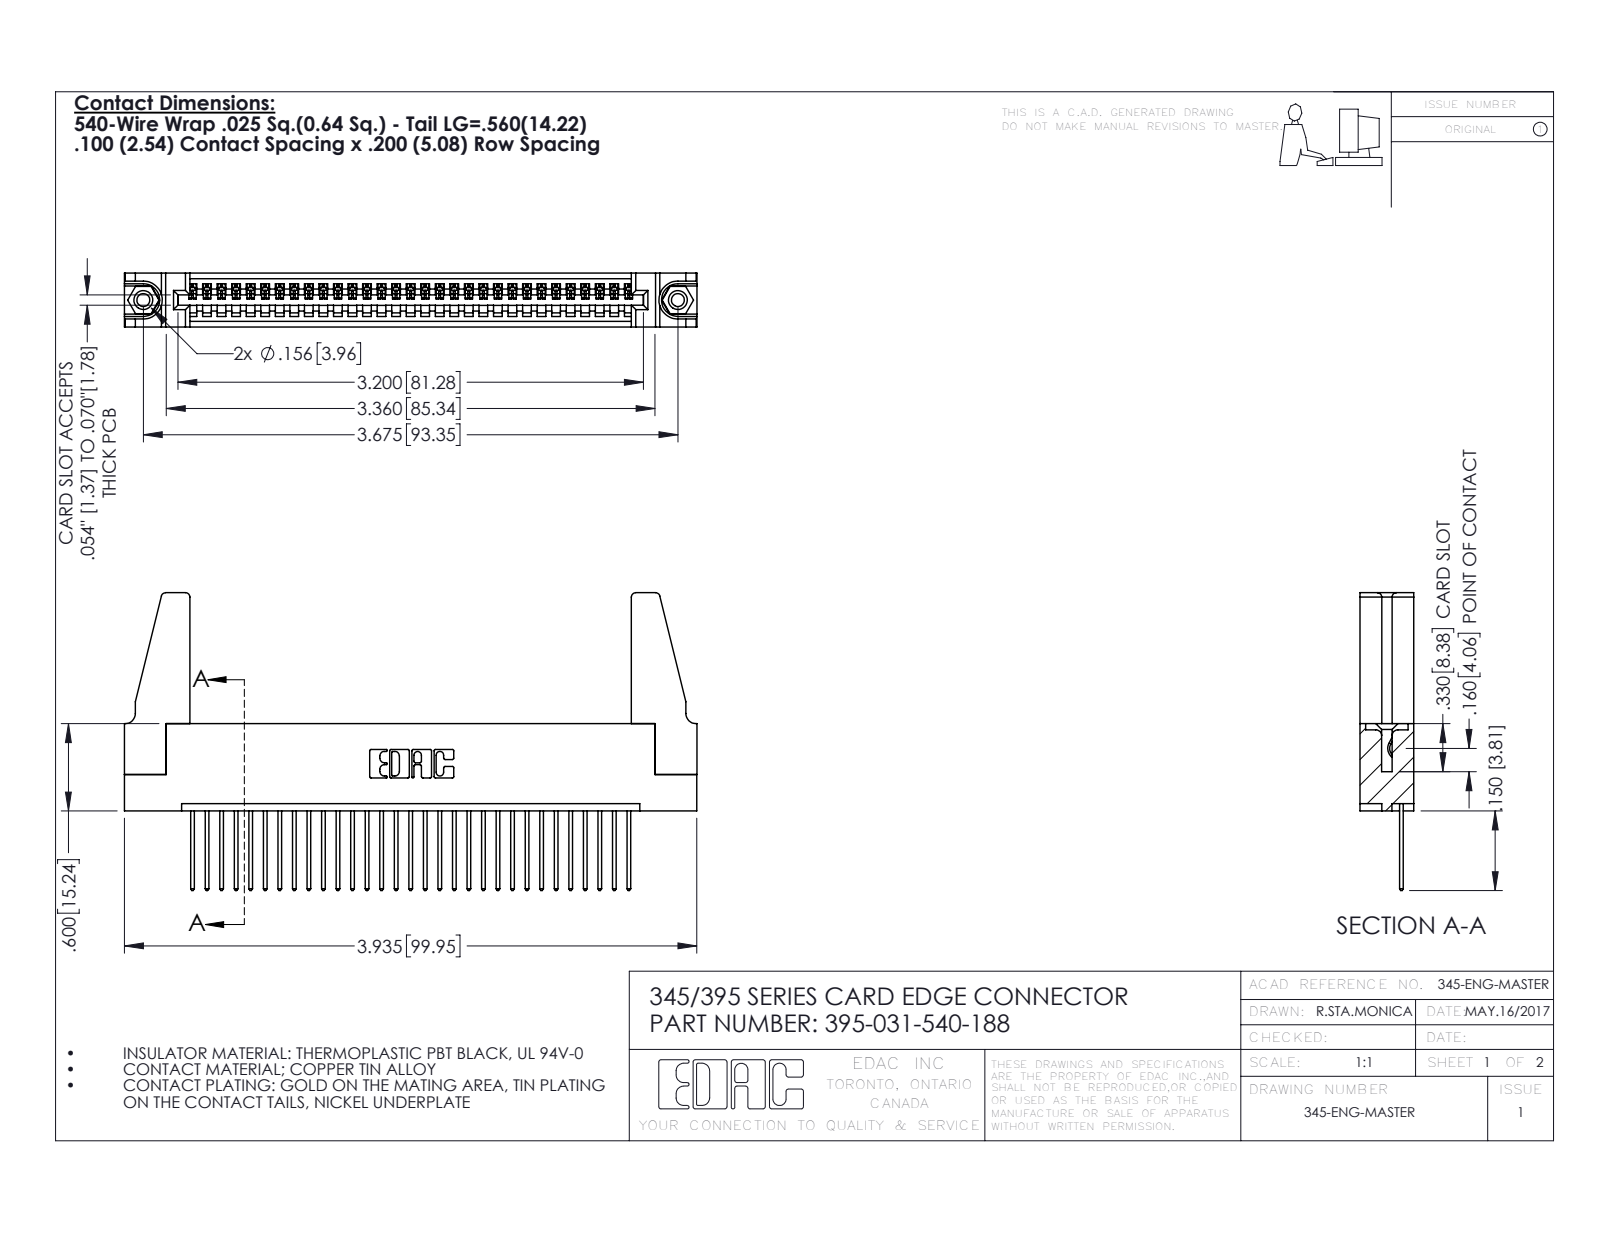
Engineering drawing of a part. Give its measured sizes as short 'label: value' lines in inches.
name: 345-250-001_345-250-001-102; 345 Part_Flush Mounting Lugs - 0.156 Dia-TH; 395-031-540-188; 345-292-001_345-293-140 (+1 more)
written by: SolidWorks 2016 (CONFIG_CONTROL_DESIGN)
unit: in
bodies: 36 solids, 2048 faces (1392 planar, 640 cylindrical, 16 other)
size: 3.936 × 2.047 × 0.37
volume: 0.775 in³; area: 24.55 in²
holes: 2× ⌀0.089, 2× ⌀0.125, 2× ⌀0.156, 1× ⌀0.064
bosses: 2× ⌀0.155
rounds: 62× R0.006, 62× R0.01, 22× R0.01, 8× R0.03, 6× R0.007, 6× R0.031, 3× R0.026, 2× R0.031
face distances: 0.072, 0.298, 0.37, 0.2, 0.098, 0.272, 0.025, 0.225, 0.149, 0.072
hole spacings: 0.27, 3.44, 3.675
